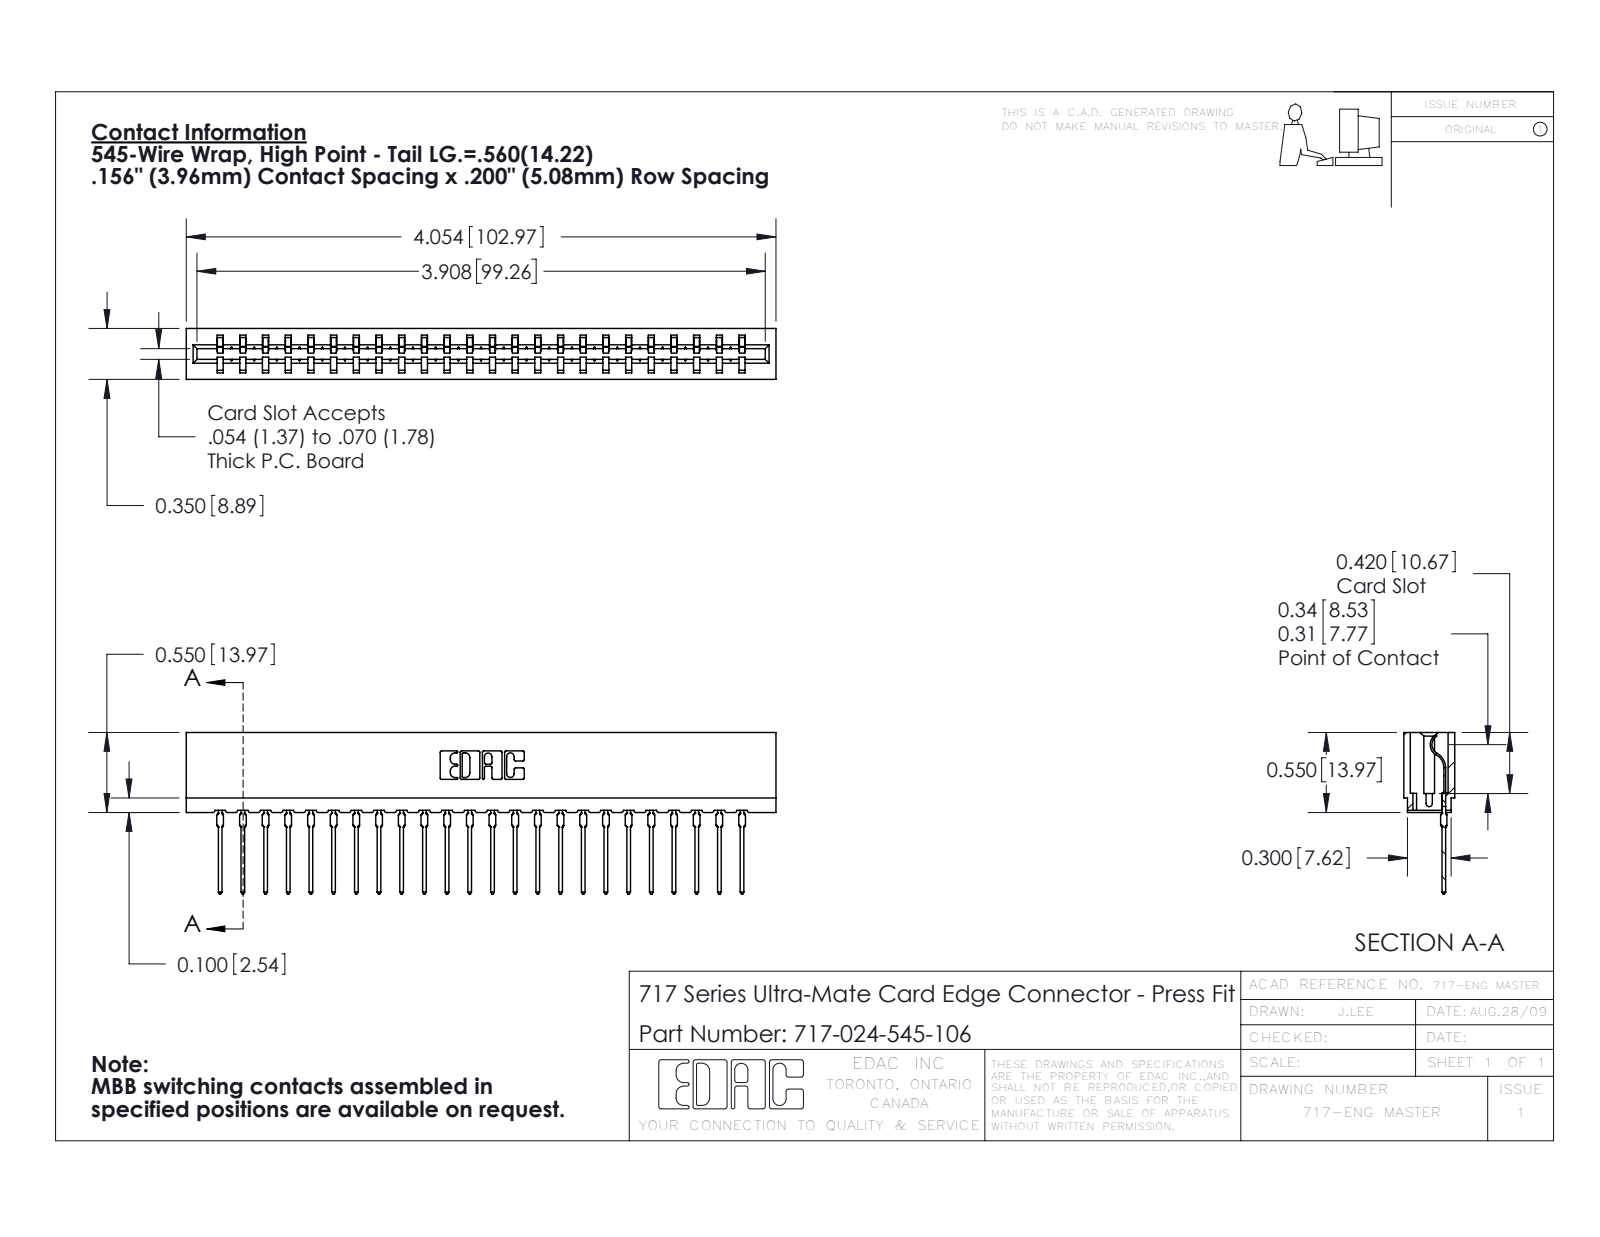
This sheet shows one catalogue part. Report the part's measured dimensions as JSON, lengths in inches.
{"part_name": "717-024-545-106; 717 Part_Insulator Option - 06; 745-292-001_545", "step_written_by": "SolidWorks 2016 (CONFIG_CONTROL_DESIGN)", "units": "inches", "bodies": {"solids": 25, "faces": 2806, "planar": 1686, "cylindrical": 496, "other": 624}, "overall_size": [4.054, 1.109, 0.35], "volume_in3": 0.54, "surface_area_in2": 19.54, "partial_cylinders_radius": [[0.015, 48], [0.021, 48], [0.01, 22], [0.007, 6], [0.031, 6], [0.005, 4], [0.011, 4], [0.026, 3]], "face_to_face_distances": [0.212, 0.138, 0.35, 0.156, 0.074, 0.063, 0.287, 0.076, 0.149, 0.624]}
